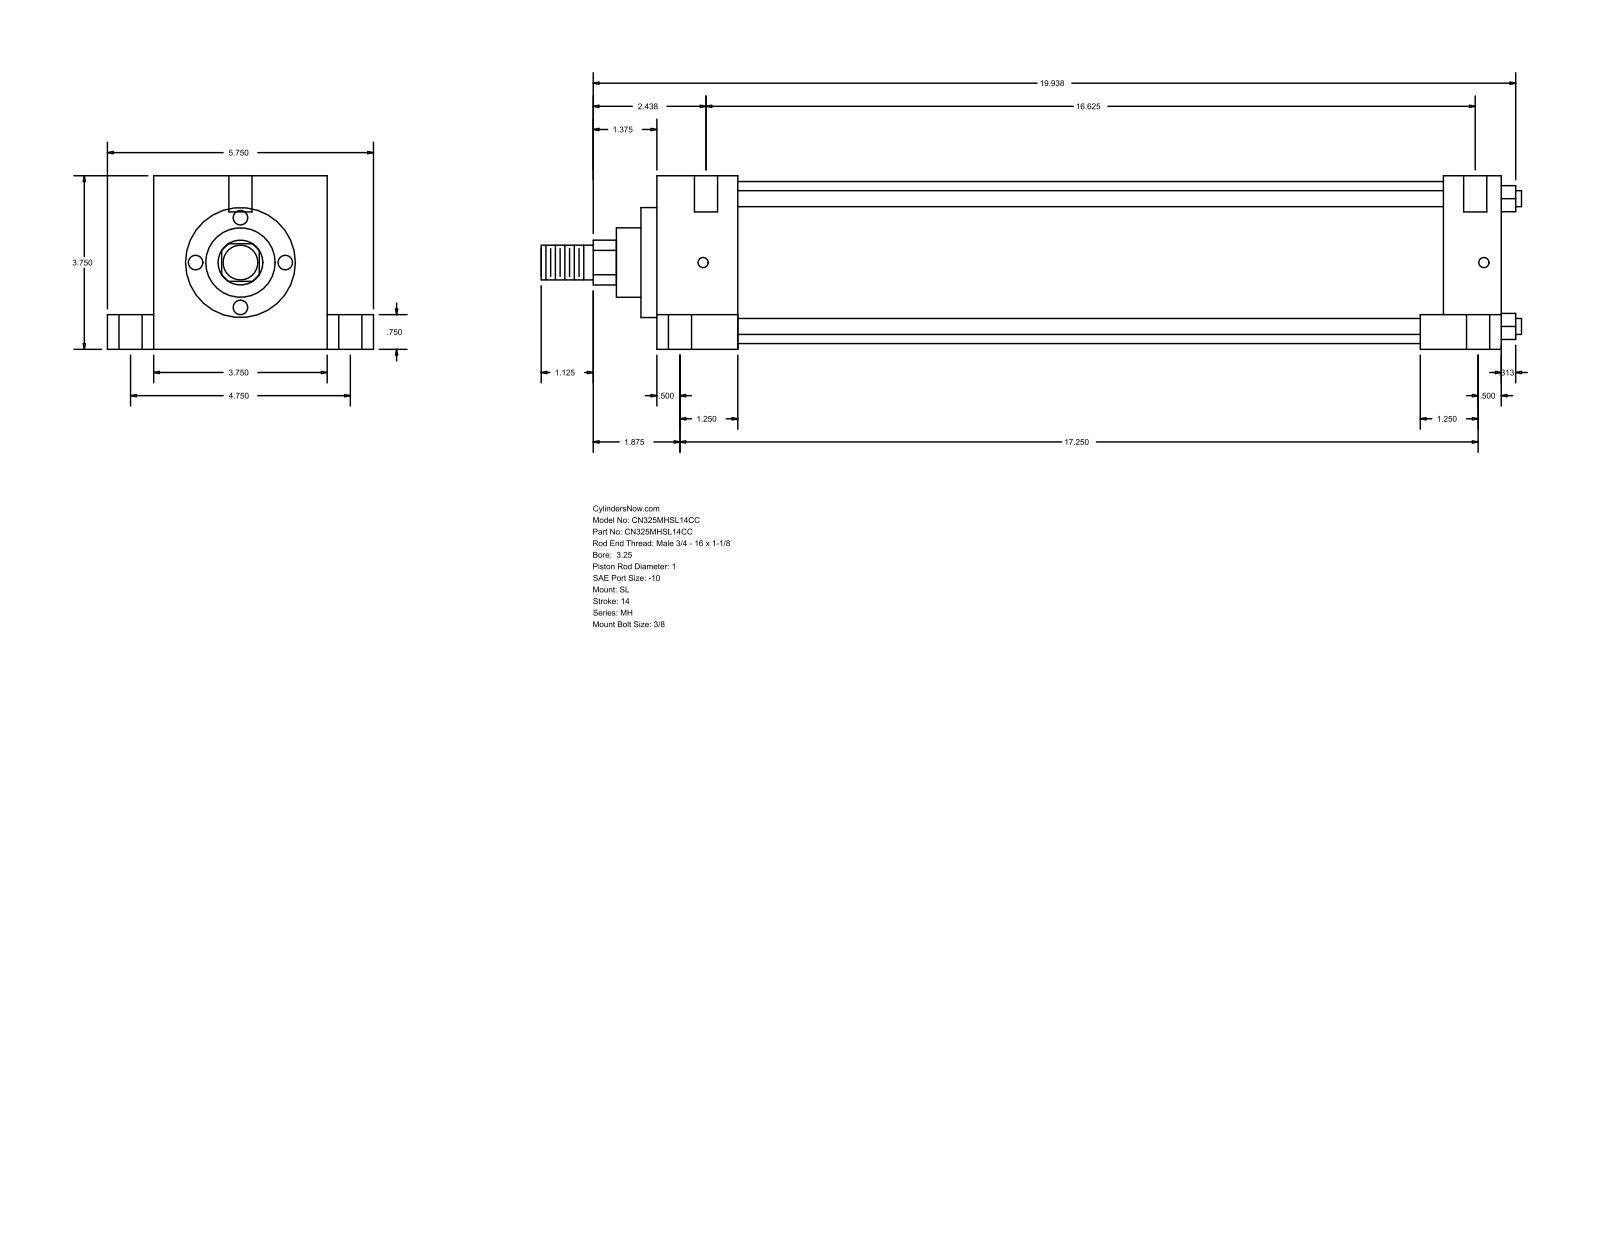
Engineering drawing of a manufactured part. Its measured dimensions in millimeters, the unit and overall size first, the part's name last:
Units: millimetres
Overall size (bounding box): 538.16 × 146.05 × 95.25
Round holes (diameter × count): ⌀12.7 ×6, ⌀5.56 ×4, ⌀19.05 ×4
Round bosses / shafts (diameter × count): ⌀8.76 ×4, ⌀88.9 ×1, ⌀60.33 ×1, ⌀38.1 ×1, ⌀25.4 ×1, ⌀19.05 ×1
Partial cylindrical surfaces — rounded edges, fillets, slot ends (radius × count): R12.29 ×1
Main face-to-face distances: 95.24, 463.56, 44.46, 419.1, 25.41, 120.65, 19.05, 76.19, 431.81, 387.35
Hole centre spacings: 60.35, 60.41, 61.65, 62, 120.66, 428.13, 428.62, 429.7
Bodies: 0 solids, 110 faces (77 planar, 33 cylindrical, 0 other)
Part name (STEP PRODUCT): MH_SL__0325_1
STEP written by: GSSL Pune (CONFIG_CONTROL_DESIGN)
